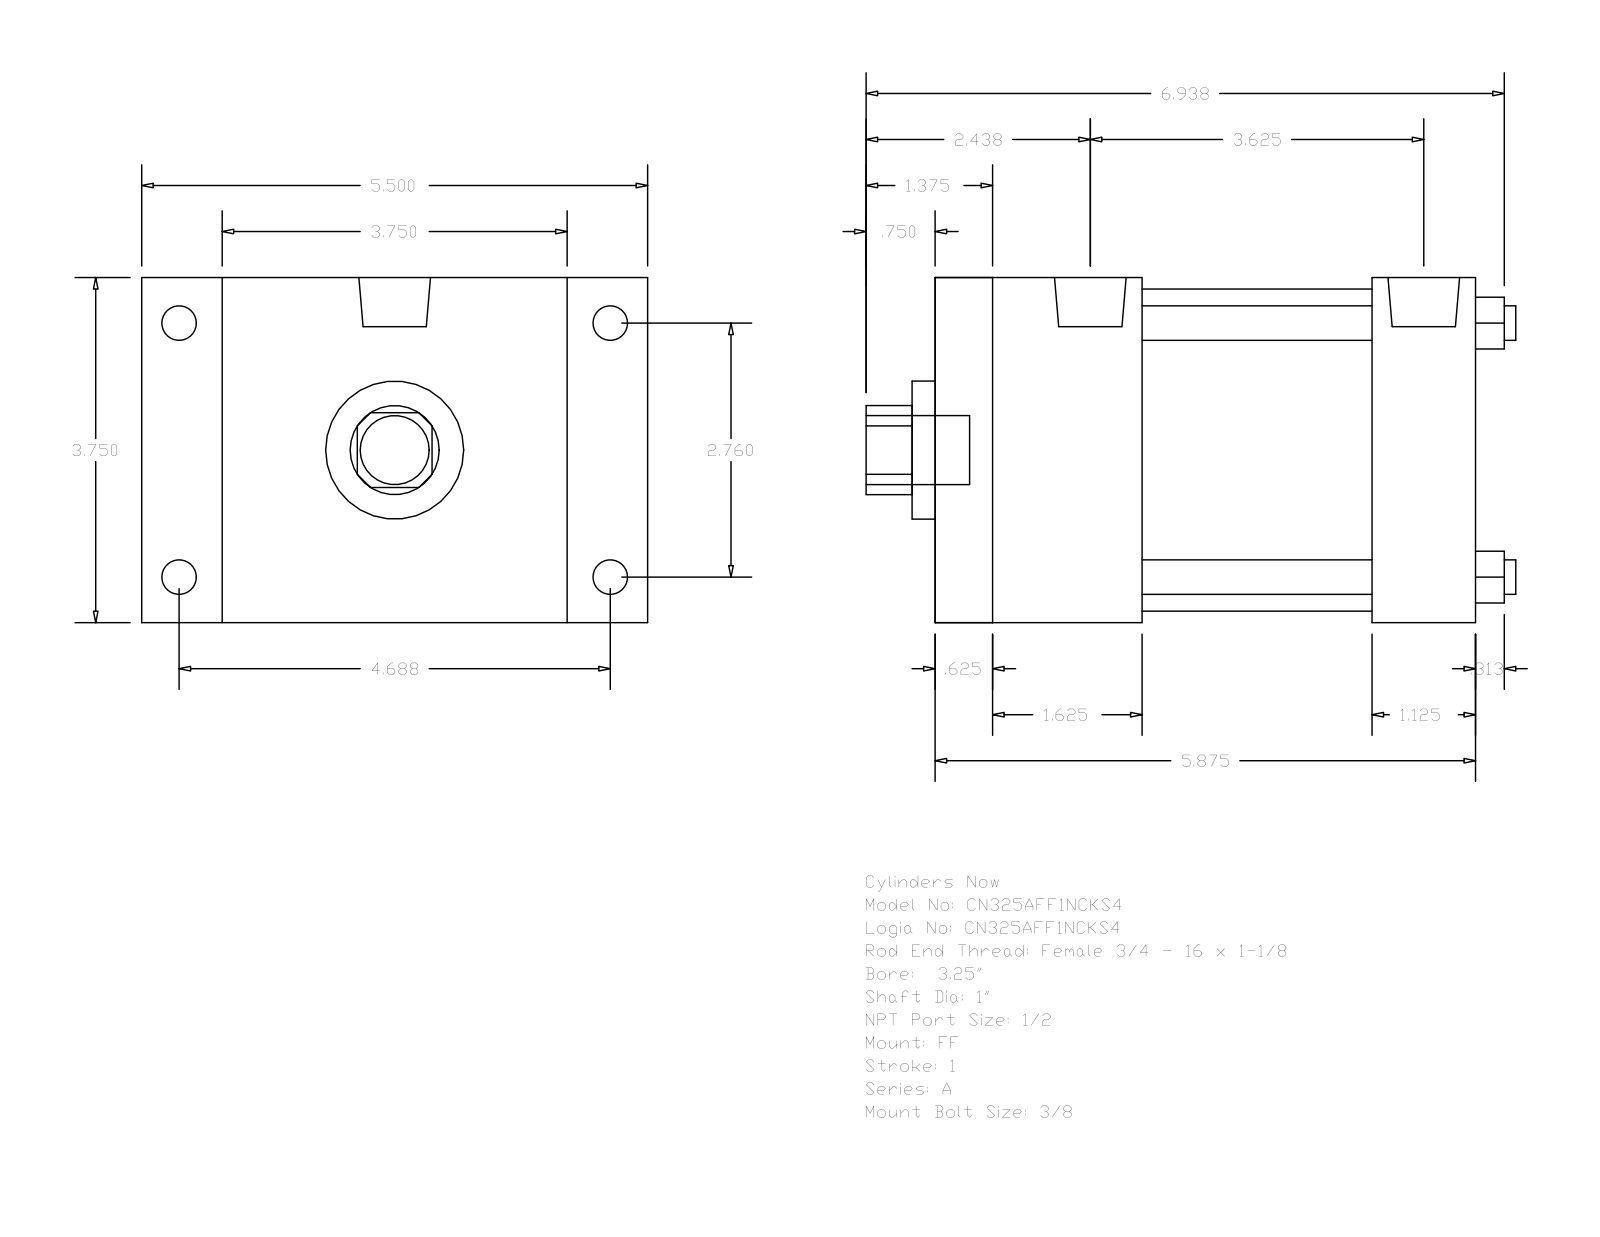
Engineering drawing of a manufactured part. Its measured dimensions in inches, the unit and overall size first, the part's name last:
Units: inches
Overall size (bounding box): 7.063 × 5.5 × 3.75
Round holes (diameter × count): ⌀0.375 ×4, ⌀1 ×1, ⌀1.5 ×1, ⌀3.5 ×1
Round bosses / shafts (diameter × count): ⌀0.375 ×4, ⌀0.344 ×4, ⌀0.778 ×2, ⌀0.75 ×1
Partial cylindrical surfaces — rounded edges, fillets, slot ends (radius × count): R0.484 ×1
Main face-to-face distances: 3.75, 5.875, 0.625, 5.25, 2.5, 0.875, 4.625, 2.25, 4.75, 1.625
Hole centre spacings: 1.952, 2.76, 3.903
Bodies: 0 solids, 92 faces (64 planar, 28 cylindrical, 0 other)
Part name (STEP PRODUCT): A_FF__0325_1
STEP written by: GSSL Pune (CONFIG_CONTROL_DESIGN)
